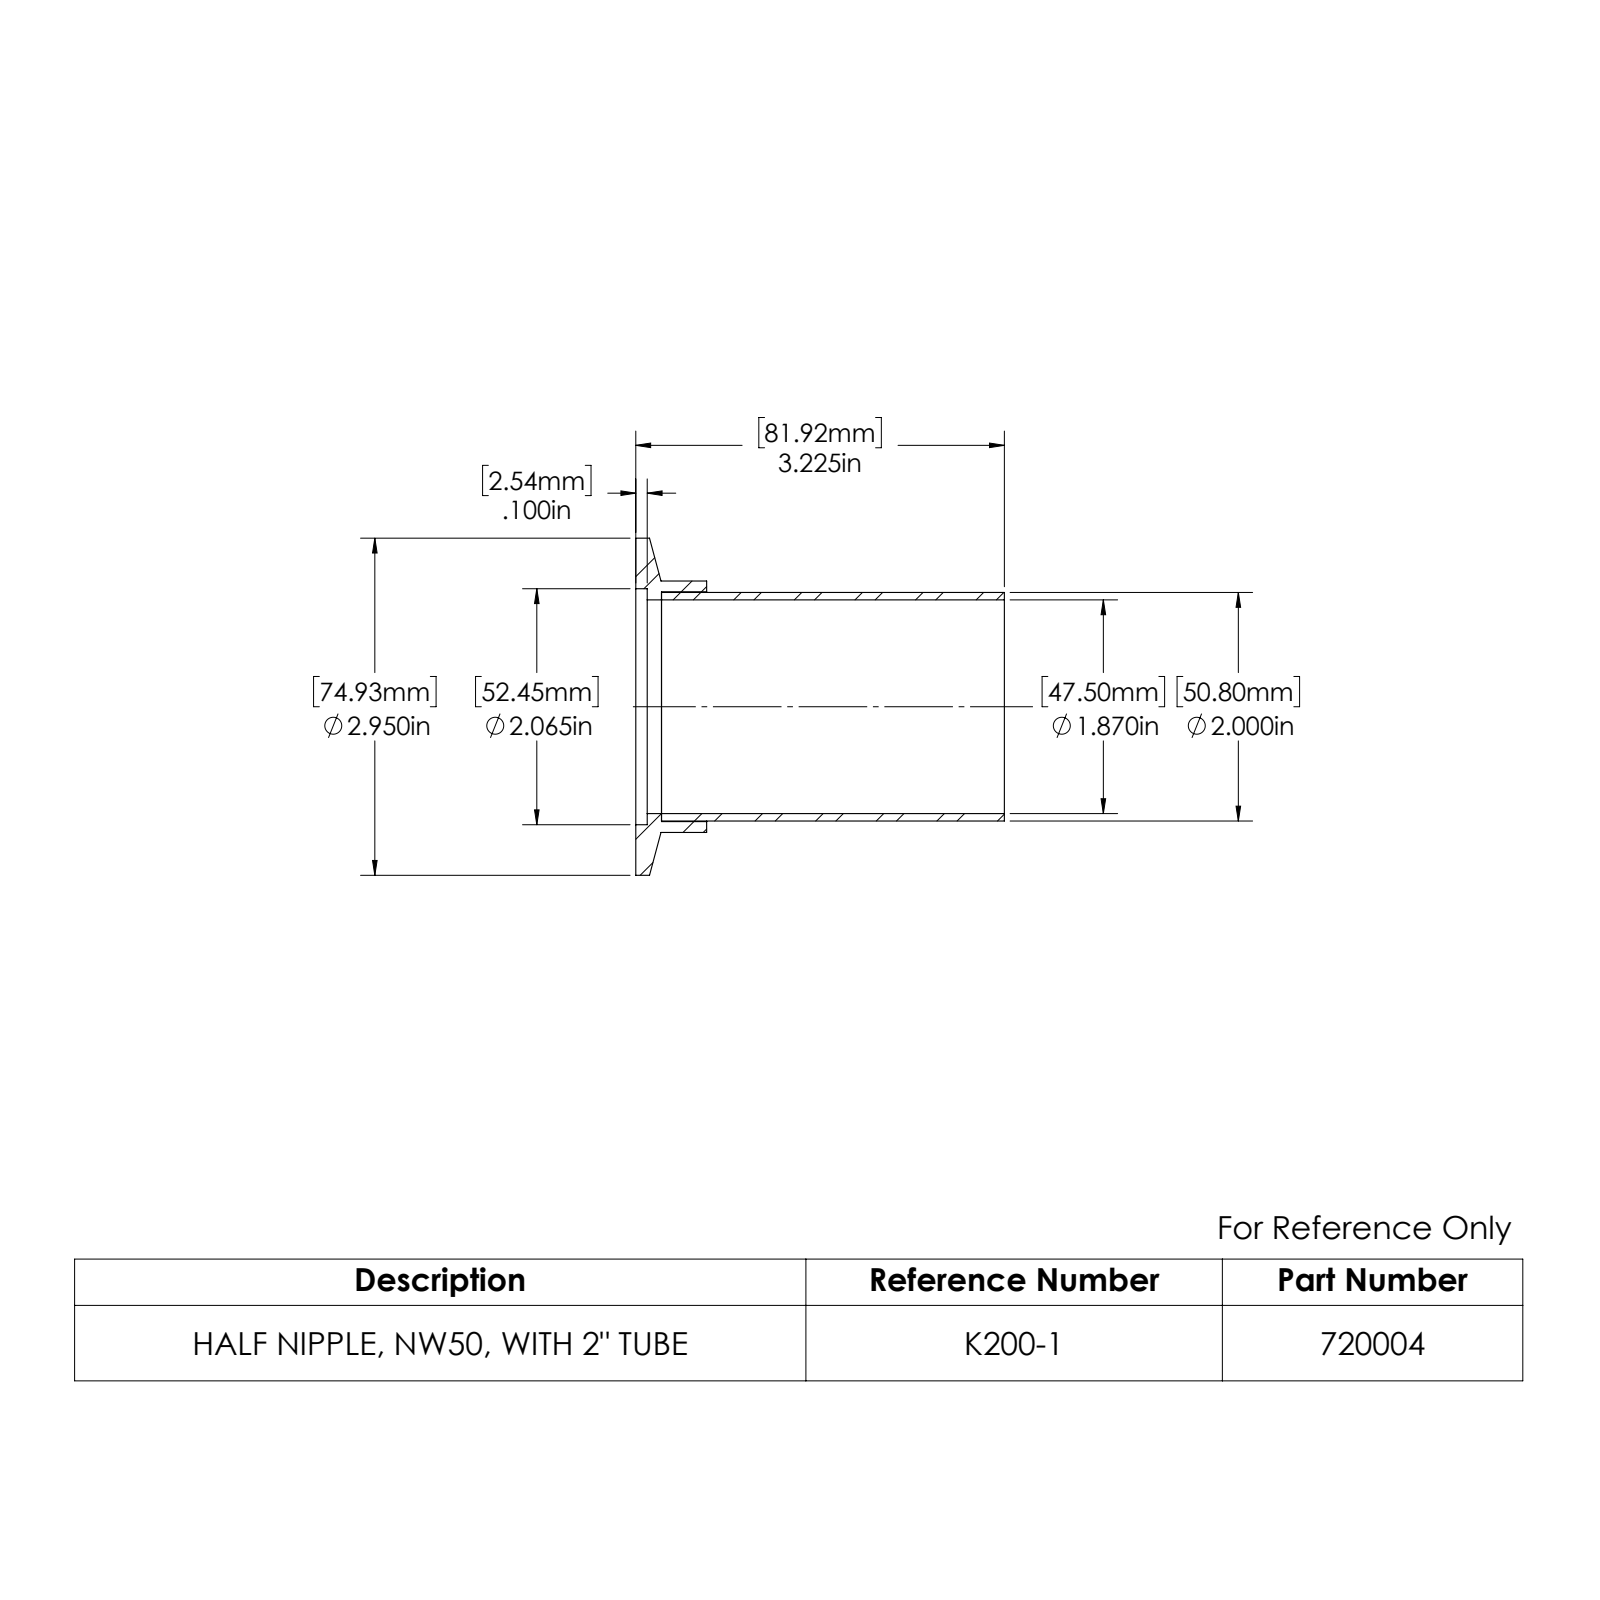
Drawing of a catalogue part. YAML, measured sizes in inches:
part_name: "940103; 720004; 713004"
step_written_by: "SolidWorks 2022 (AUTOMOTIVE_DESIGN)"
units: inches
bodies: {solids: 2, faces: 22, planar: 6, cylindrical: 14, other: 2}
overall_size: [3.225, 2.95, 2.95]
volume: 2.12
surface_area: 53.3
round_holes:
  - {diameter: 1.87, count: 1}
  - {diameter: 2.01, count: 1}
  - {diameter: 2.065, count: 1}
round_bosses_or_shafts:
  - {diameter: 2.95, count: 1}
  - {diameter: 2.2, count: 1}
  - {diameter: 2, count: 1}
face_to_face_distances: [0.225, 0.62, 0.395, 0.1, 0.125, 0.52, 3.225, 3.125, 3, 2.605]
